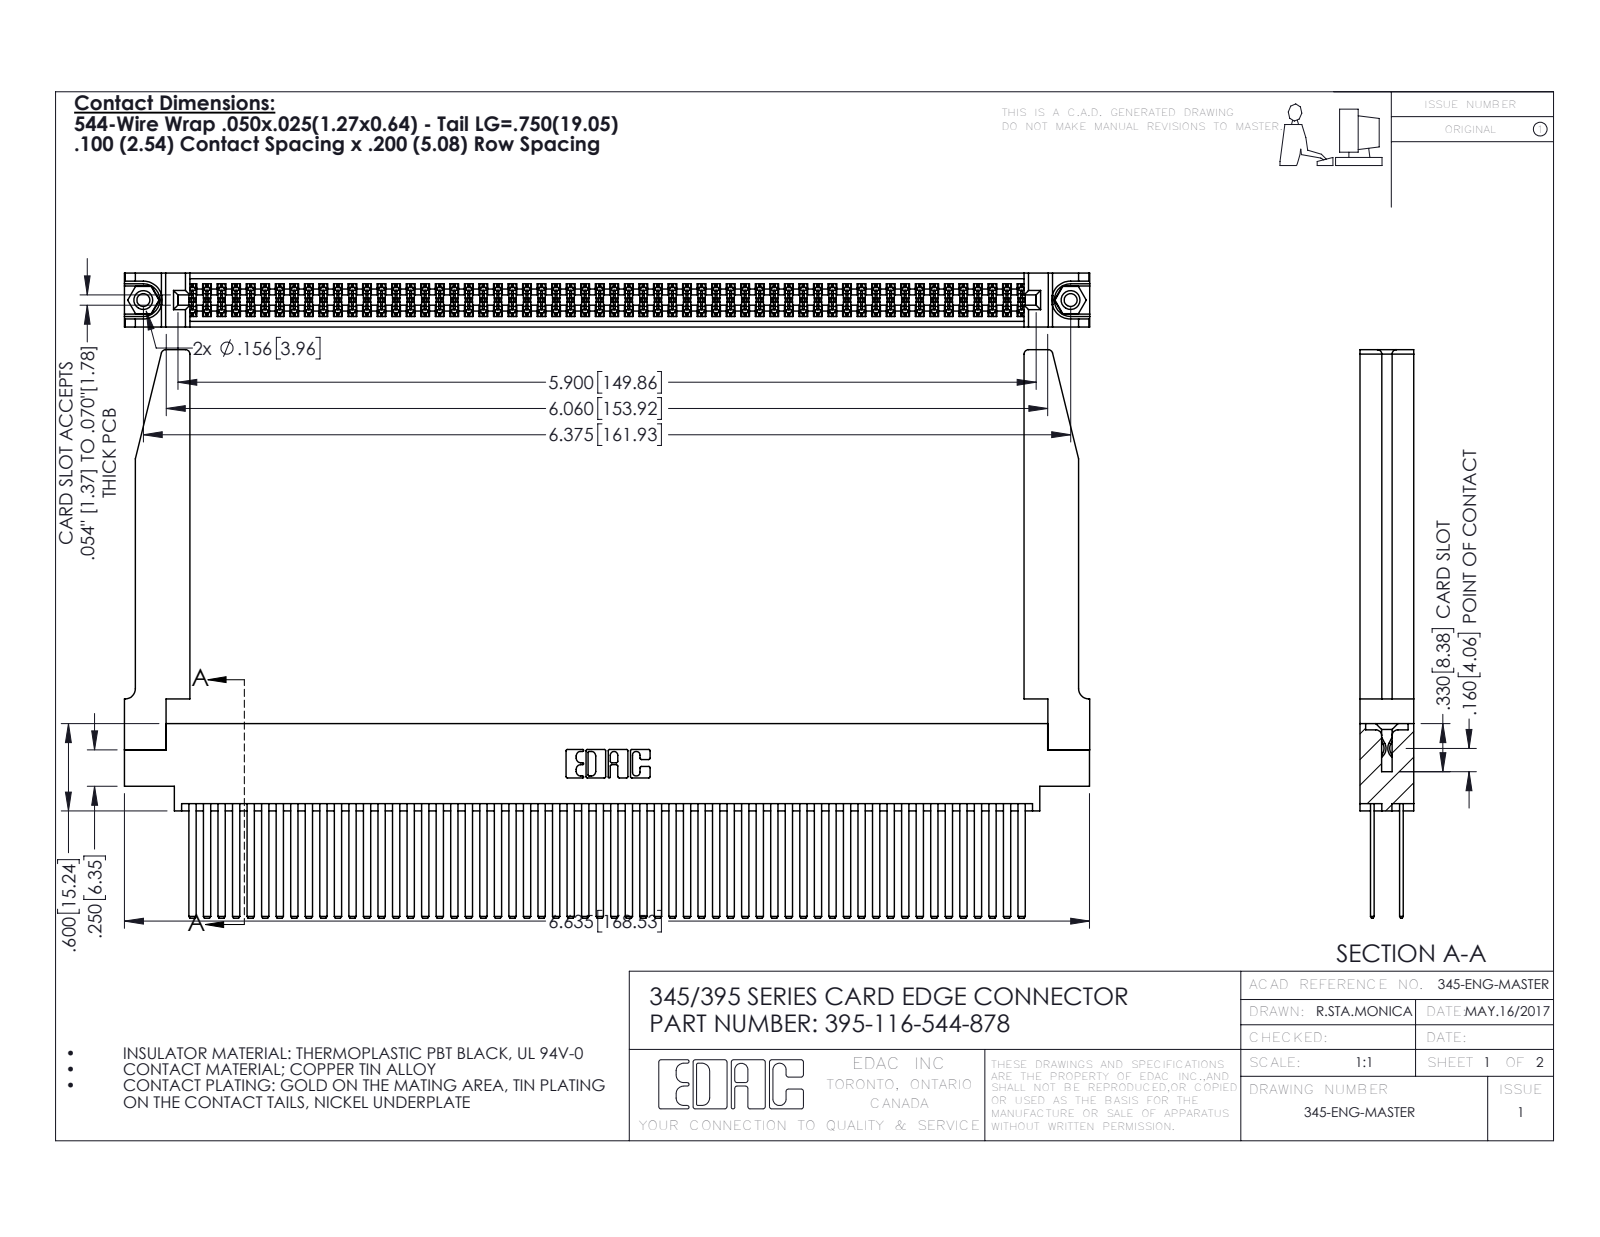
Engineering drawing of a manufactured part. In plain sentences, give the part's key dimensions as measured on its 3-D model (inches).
The part is named "345-220-078_345-220-078; 395-116-544-878; 345-292-001_345-293-144; 345 Part_0.170 Offset - 0.156 Dia-TH (+1 more)". Its 3-D file was written by "SolidWorks 2016 (CONFIG_CONTROL_DESIGN)". It is 121 solids with 5468 faces: 3590 planar, 1826 cylindrical and 52 other. Overall it measures 6.636 by 3.907 by 0.37 inches. Its volume is 1.575 cubic inches and its surface area 60.01 square inches. Round holes: 2 of diameter 0.089, 2 of diameter 0.125, 2 of diameter 0.156, 1 of diameter 0.064. Round bosses or shafts: 2 of diameter 0.155. Partial cylindrical surfaces (rounded edges, fillets, slot ends): 174 of radius 0.006, 22 of radius 0.01, 8 of radius 0.03, 6 of radius 0.007, 6 of radius 0.031, 3 of radius 0.026, 2 of radius 0.014, 2 of radius 0.019. The main face-to-face distances are 0.072, 0.298, 0.098, 0.272, 0.025, 0.2, 0.37, 0.225, 0.175, 0.15. The hole center spacings are 0.27, 6.139, 6.375.
